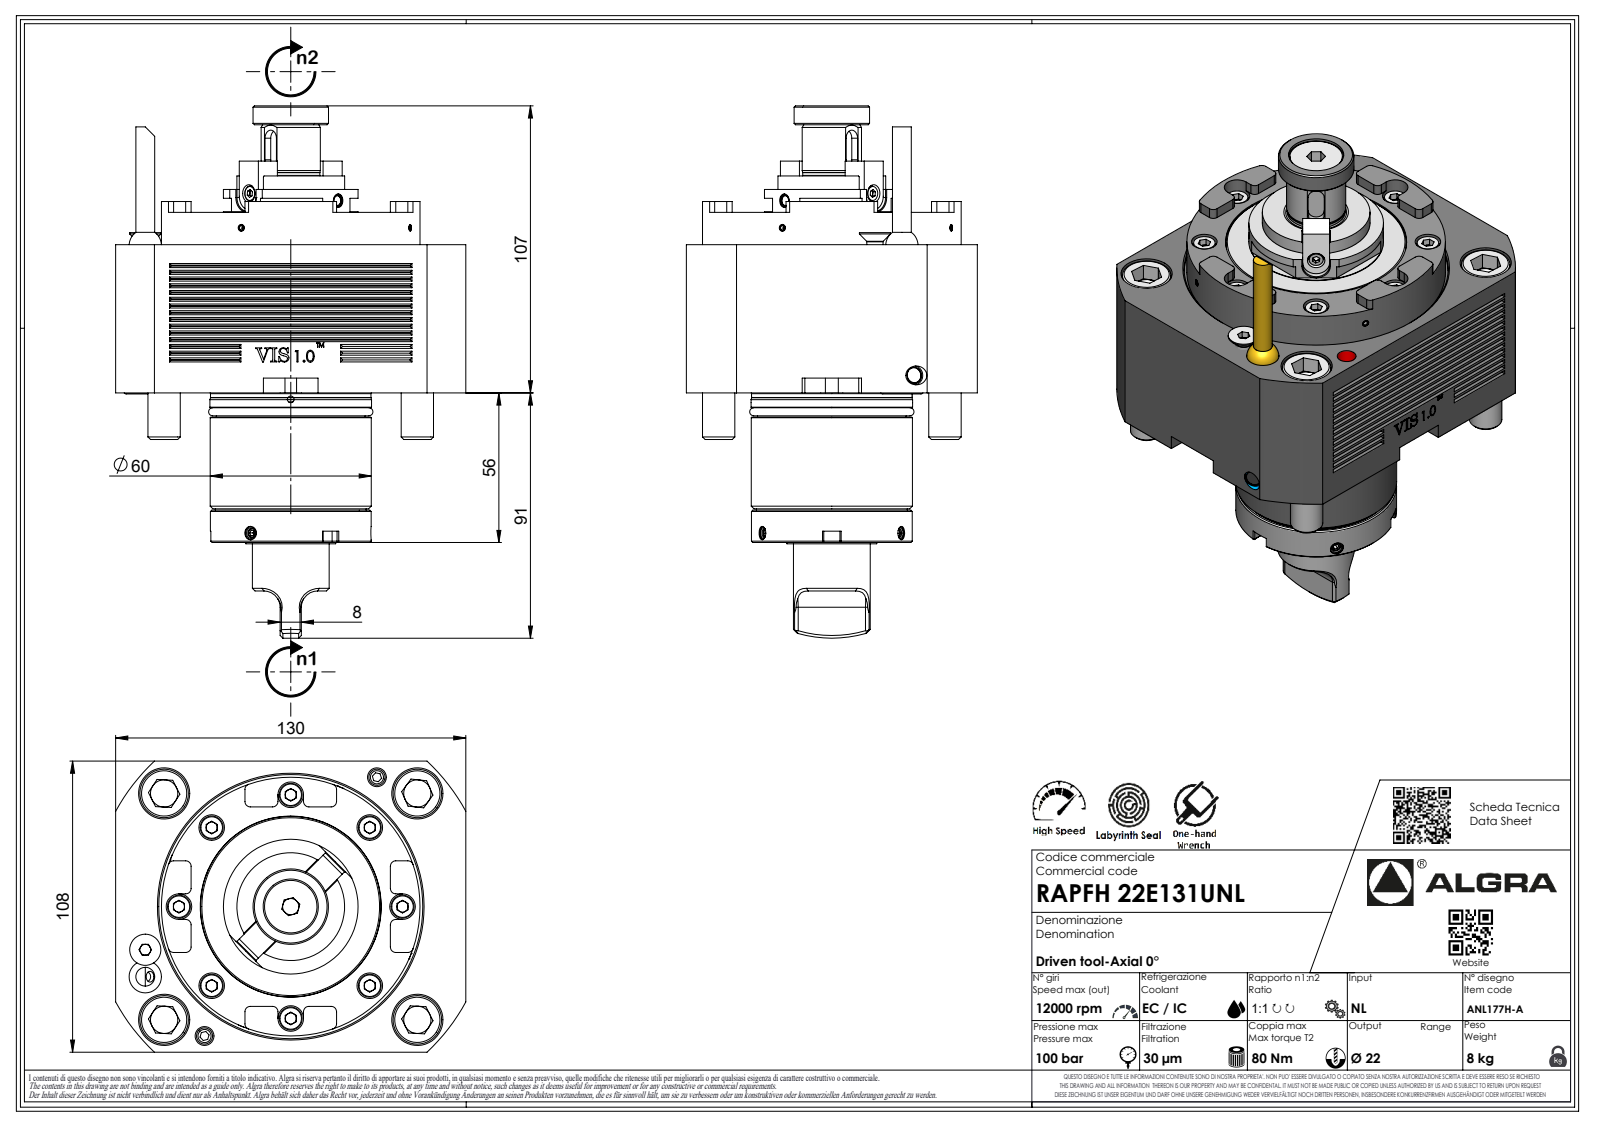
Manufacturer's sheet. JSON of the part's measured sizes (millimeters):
{"part_name": "RAPFH22E131UNL", "step_written_by": "SolidWorks 2023 (AUTOMOTIVE_DESIGN)", "units": "millimeters", "bodies": {"solids": 1, "faces": 518, "planar": 339, "cylindrical": 94, "other": 85}, "overall_size": [197.5, 130, 108], "volume_mm3": 1044000, "surface_area_mm2": 79722, "round_holes": [[2.1, 1], [4, 1]], "round_bosses_or_shafts": [[12, 4], [96, 1], [60, 1], [50, 1], [40, 1], [28.5, 1], [28, 1], [22, 1]], "partial_cylinders_radius": [[2, 25], [8, 8], [0.33, 7], [0.52, 7], [3.7, 7], [6, 6], [4.75, 4], [5, 3]], "face_to_face_distances": [55, 108, 12, 67, 130, 55.5, 110.5, 122.5, 61.5, 5.5]}
